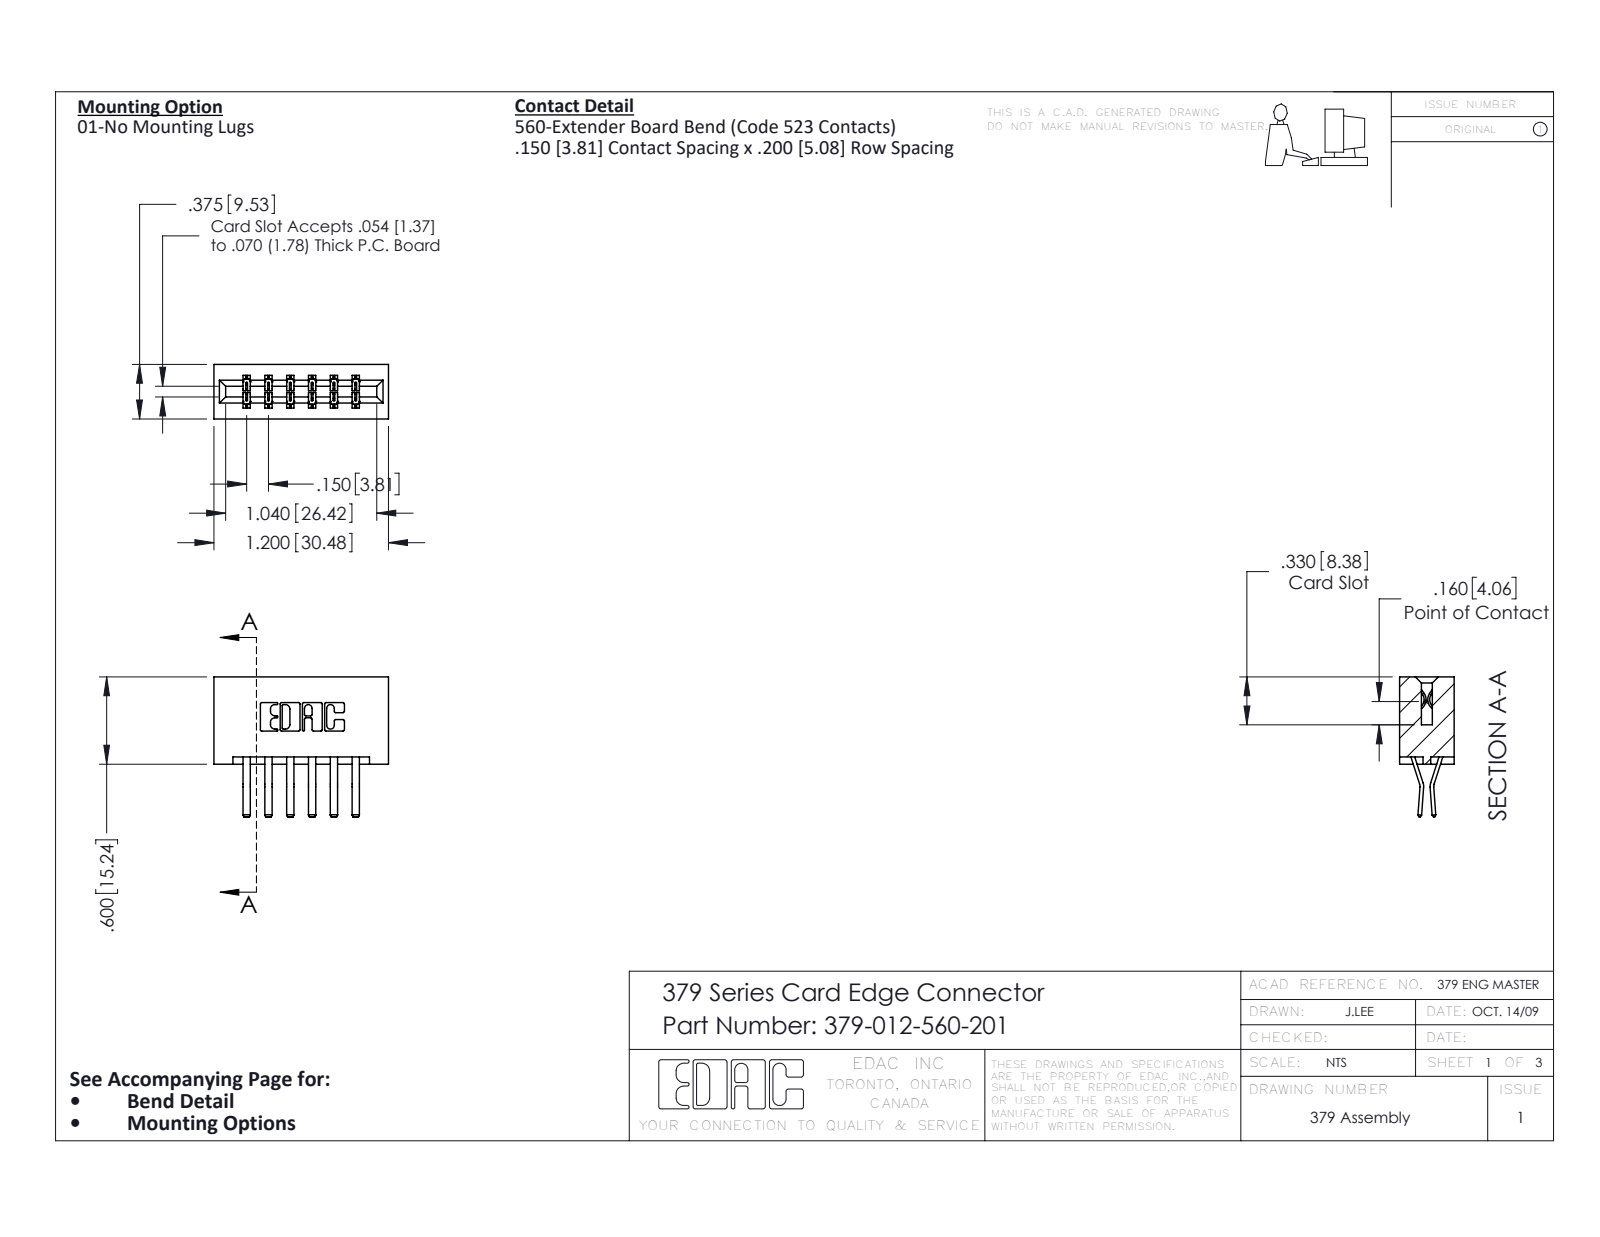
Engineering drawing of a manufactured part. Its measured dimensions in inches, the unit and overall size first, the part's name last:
Units: inches
Overall size (bounding box): 1.2 × 0.962 × 0.375
Partial cylindrical surfaces — rounded edges, fillets, slot ends (radius × count): R0.01 ×22, R0.006 ×18, R0.007 ×6, R0.031 ×6, R0.026 ×3, R0.01 ×2, R0.014 ×2, R0.022 ×2
Main face-to-face distances: 0.3, 0.15, 0.2, 0.05, 0.1, 0.55, 0.375, 0.25, 0.35, 0.45
Volume: 0.22 in³ · Surface area: 6.191 in²
Bodies: 13 solids, 754 faces (498 planar, 256 cylindrical, 0 other)
Part name (STEP PRODUCT): 379 Part_Lugless; 379-012-560-201; 345-292-001_560 Tail
STEP written by: SolidWorks 2016 (CONFIG_CONTROL_DESIGN)
